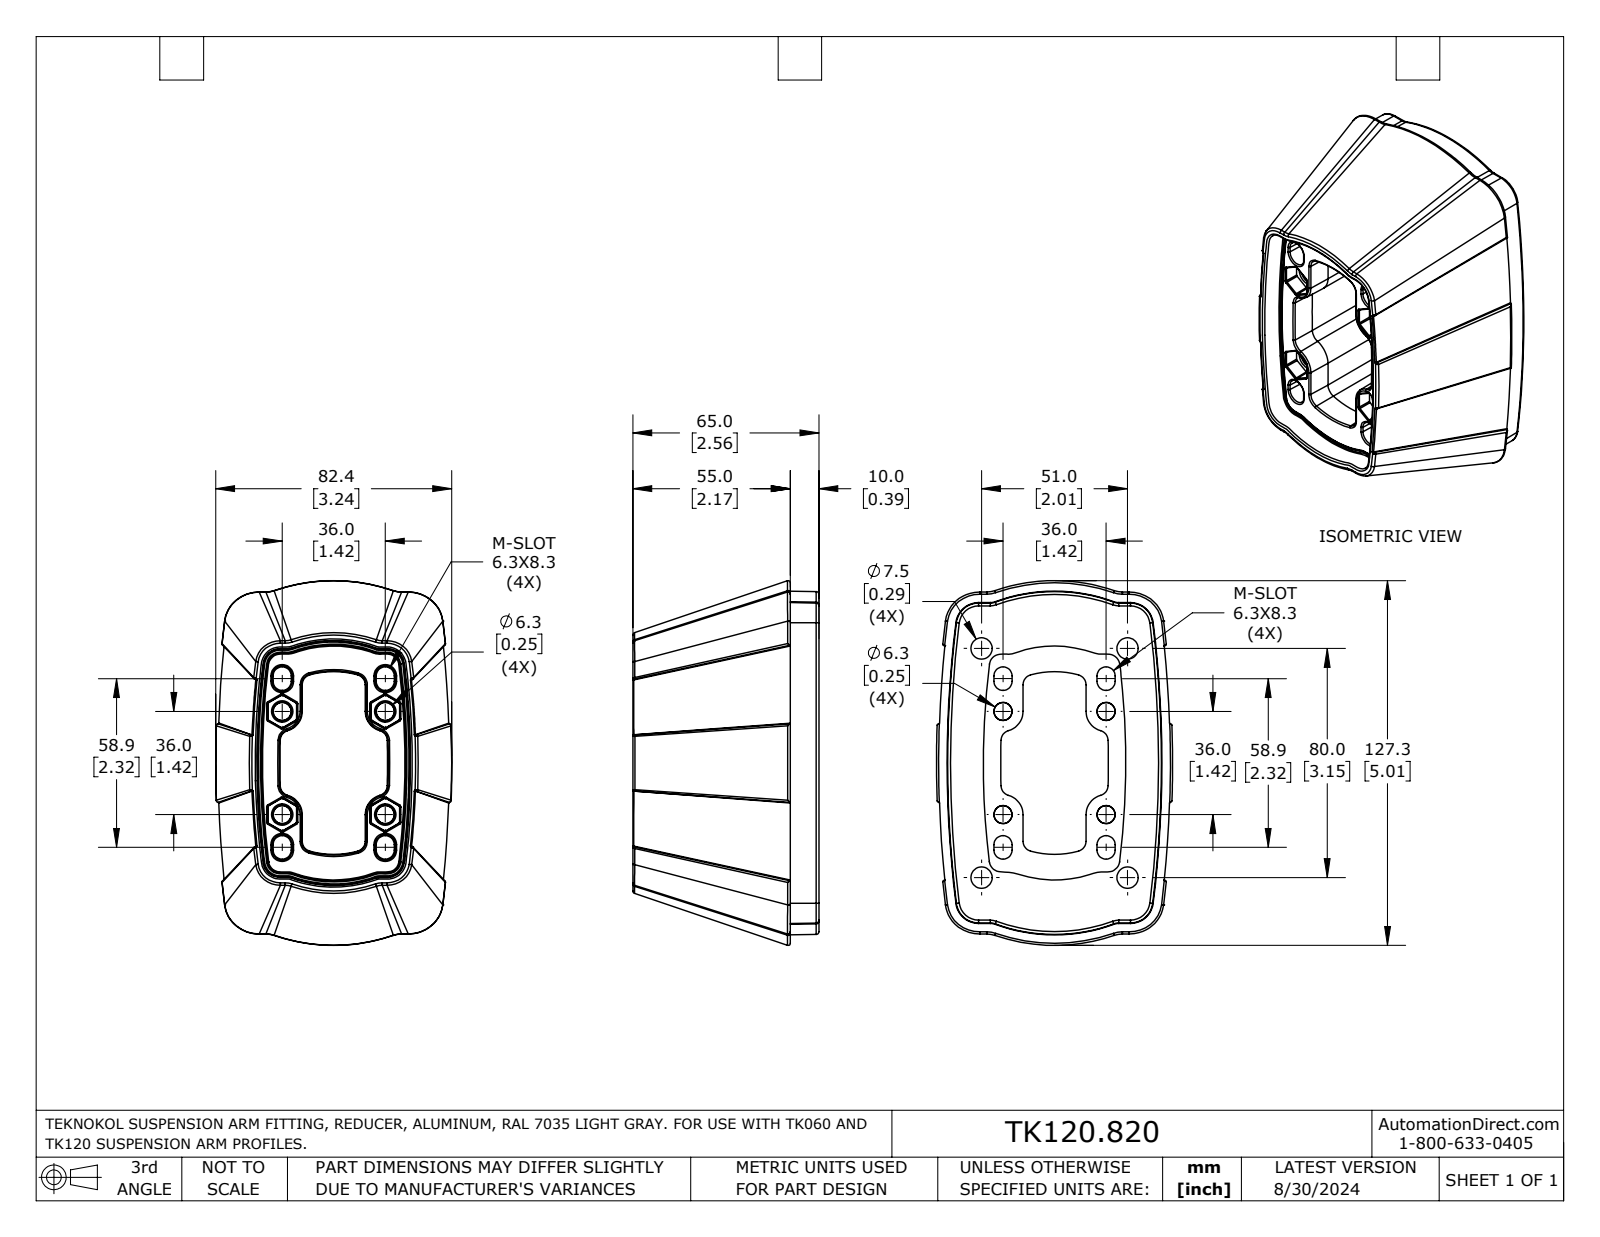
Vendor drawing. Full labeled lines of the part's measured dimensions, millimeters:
Part name (STEP PRODUCT): TK120.820
STEP written by: SolidWorks 2023 (AUTOMOTIVE_DESIGN)
Units: millimetres
Bodies: 1 solid, 399 faces (74 planar, 104 cylindrical, 221 other)
Overall size (bounding box): 127.4 × 82.4 × 65
Volume: 282 300 mm³ · Surface area: 52 500 mm²
Round holes (diameter × count): ⌀6.3 ×4, ⌀7.4 ×4
Partial cylindrical surfaces — rounded edges, fillets, slot ends (radius × count): R0.5 ×28, R0.4 ×20, R3.2 ×8, R3.6 ×8, R7.1 ×4, R0.5 ×2, R0.8 ×2, R0.9 ×2
Main face-to-face distances: 10, 47.8, 57.7, 22, 36, 7.3, 55, 65, 10.2, 32.2
Hole centre spacings: 23.2, 36, 48.7, 58.5, 72.5, 50.9, 51, 80
